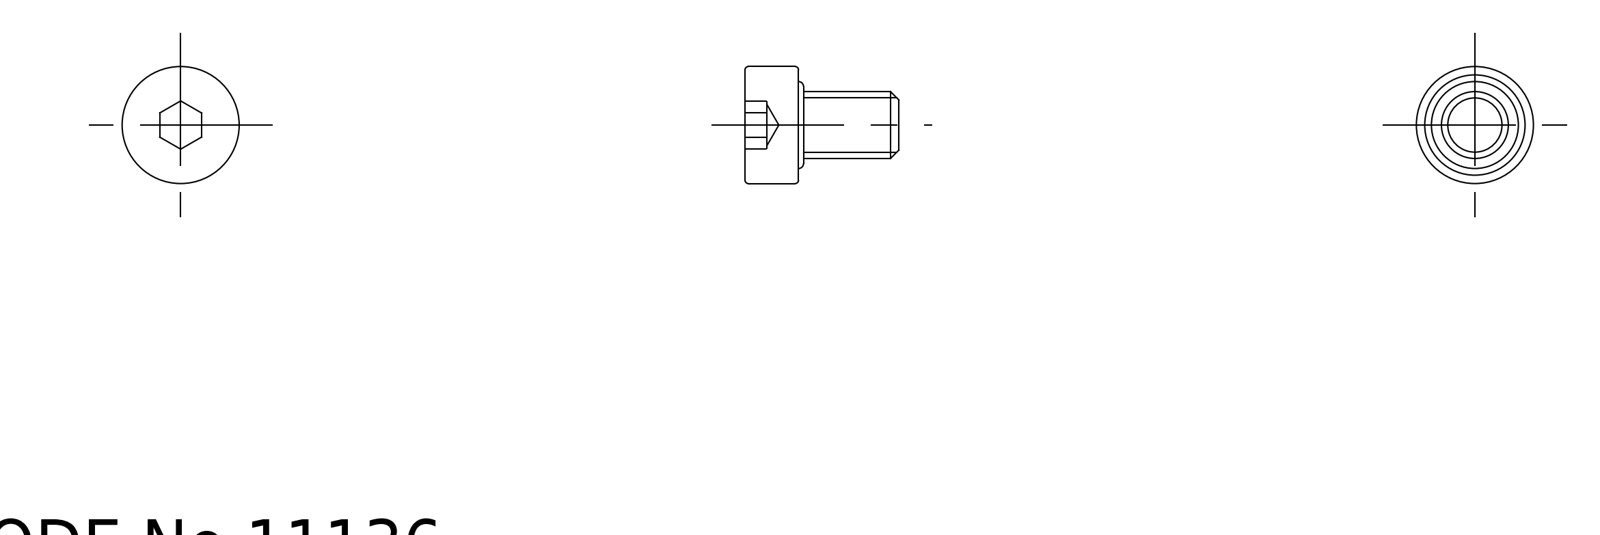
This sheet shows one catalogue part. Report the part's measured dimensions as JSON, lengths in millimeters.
{"part_name": "screw; TL_418_M4_6", "step_written_by": "SolidWorks 2015 (AUTOMOTIVE_DESIGN)", "units": "millimeters", "bodies": {"solids": 2, "faces": 27, "planar": 11, "cylindrical": 6, "other": 10}, "overall_size": [9.2, 7, 7], "volume_mm3": 189, "surface_area_mm2": 263, "round_holes": [[6, 1]], "round_bosses_or_shafts": [[7, 1], [4, 1]], "face_to_face_distances": [2.9, 9.2, 6.3, 3.2, 6, 2.5, 1.3, 1.6, 1.9, 7.9]}
